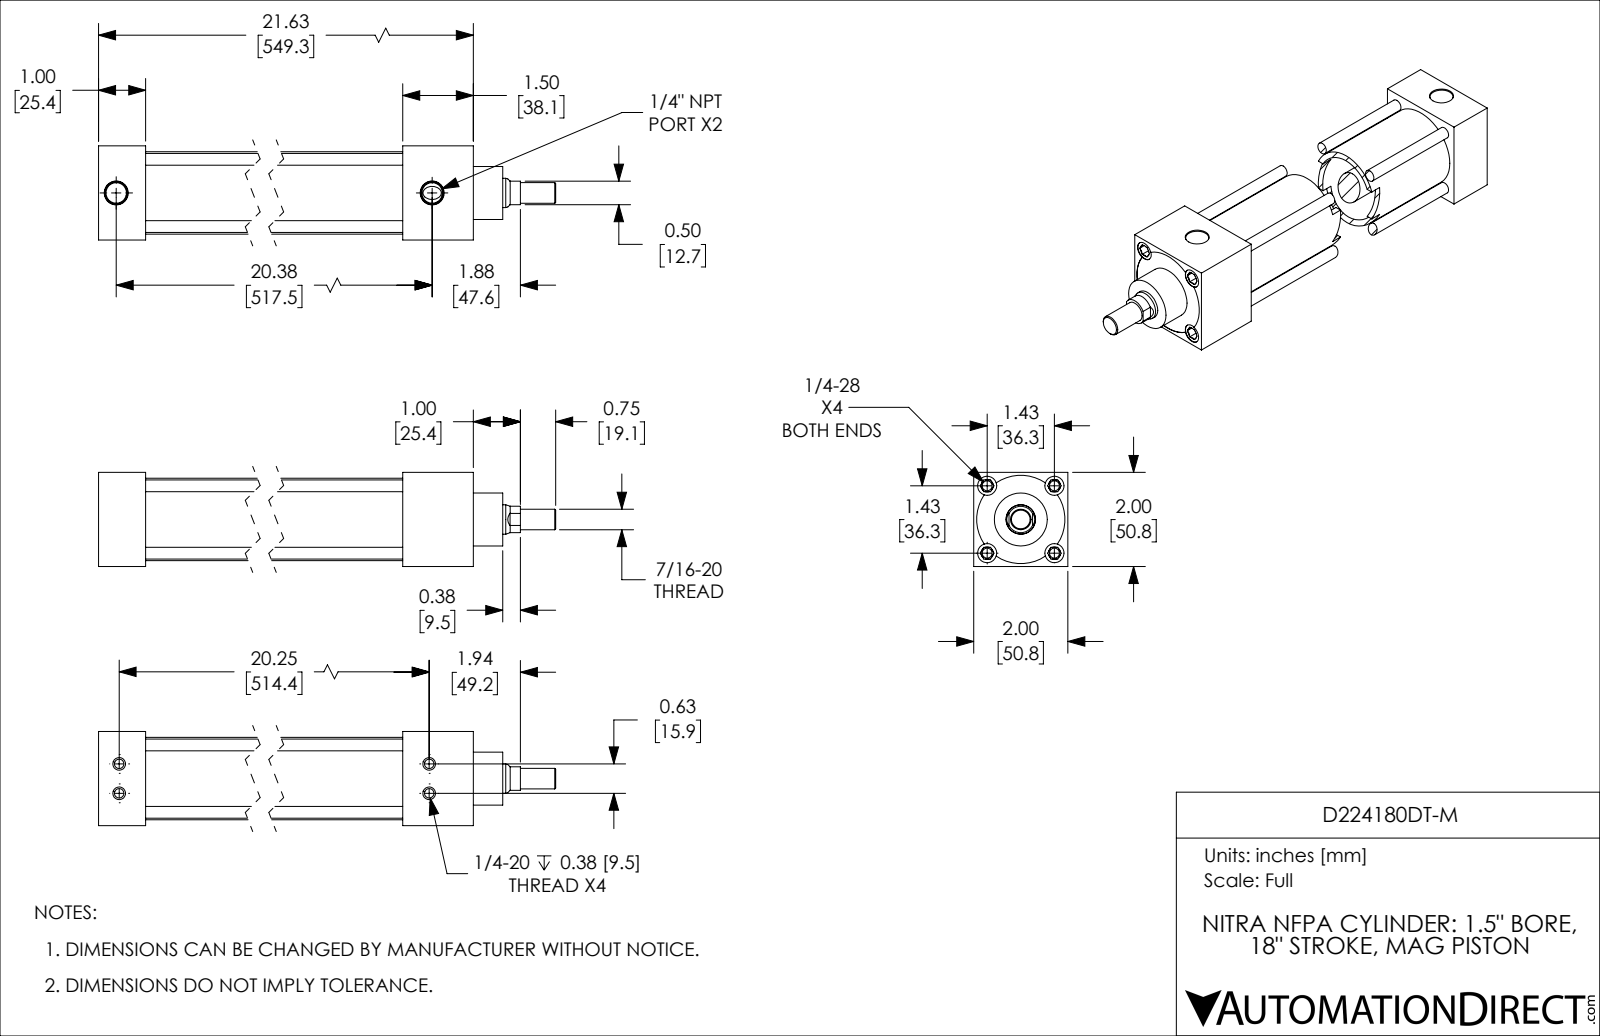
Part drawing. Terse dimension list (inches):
name: D224180DT-M_PISTON_KK1; D224180DT-M; D224180DT-M_BODY
written by: SolidWorks 2019 (CONFIG_CONTROL_DESIGN)
unit: in
bodies: 2 solids, 203 faces (58 planar, 65 cylindrical, 80 other)
size: 23.375 × 2 × 2
volume: 33.71 in³; area: 353 in²
holes: 4× ⌀0.201, 4× ⌀0.213, 4× ⌀0.406, 2× ⌀0.438, 1× ⌀0.626, 1× ⌀1.501
bosses: 4× ⌀0.25, 1× ⌀1.751, 1× ⌀1.499, 1× ⌀1.125, 1× ⌀0.624, 1× ⌀0.437
rounds: 1× R0.281, 1× R0.937
face distances: 2, 1, 20.125, 19.125, 2.125, 21.62, 20.62, 1.495, 1.125, 18
hole spacings: 0.319, 1.011, 1.43, 0.625, 2.022, 20.25, 20.26, 20.315
